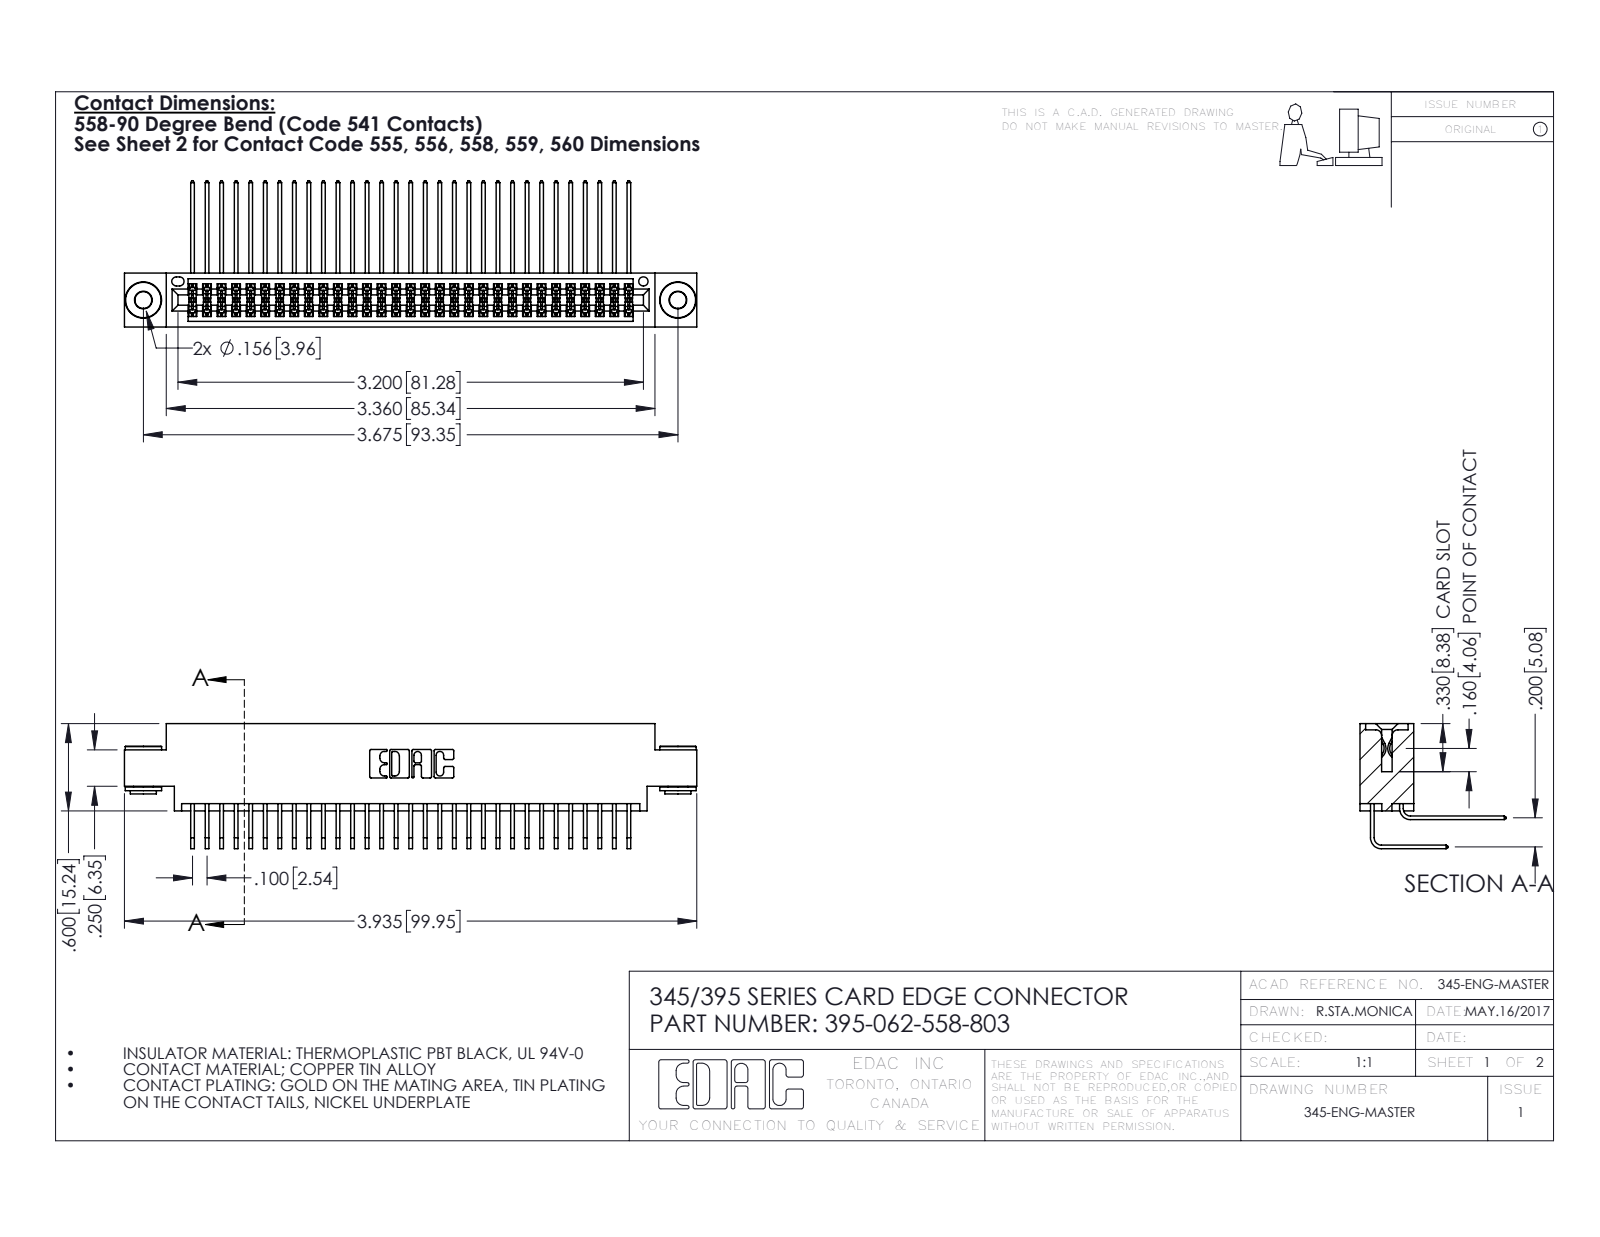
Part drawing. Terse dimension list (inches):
name: 345-250-002_345-250-002-102; 395-062-558-803; 345-292-001_558 559 Tail - 1; 345-292-001_558 Tail - 2 (+1 more)
written by: SolidWorks 2016 (CONFIG_CONTROL_DESIGN)
unit: in
bodies: 65 solids, 3392 faces (2264 planar, 1120 cylindrical, 8 other)
size: 3.935 × 1.005 × 0.859
volume: 0.602 in³; area: 25.43 in²
holes: 2× ⌀0.116, 2× ⌀0.156, 1× ⌀0.064
bosses: 2× ⌀0.25, 2× ⌀0.18, 2× ⌀0.136
rounds: 94× R0.006, 22× R0.01, 6× R0.007, 6× R0.031, 3× R0.026, 2× R0.014, 2× R0.019, 2× R0.022
face distances: 0.072, 0.298, 0.2, 0.37, 0.098, 0.272, 0.025, 0.225, 0.175, 0.025
hole spacings: 0.27, 3.44, 3.675
